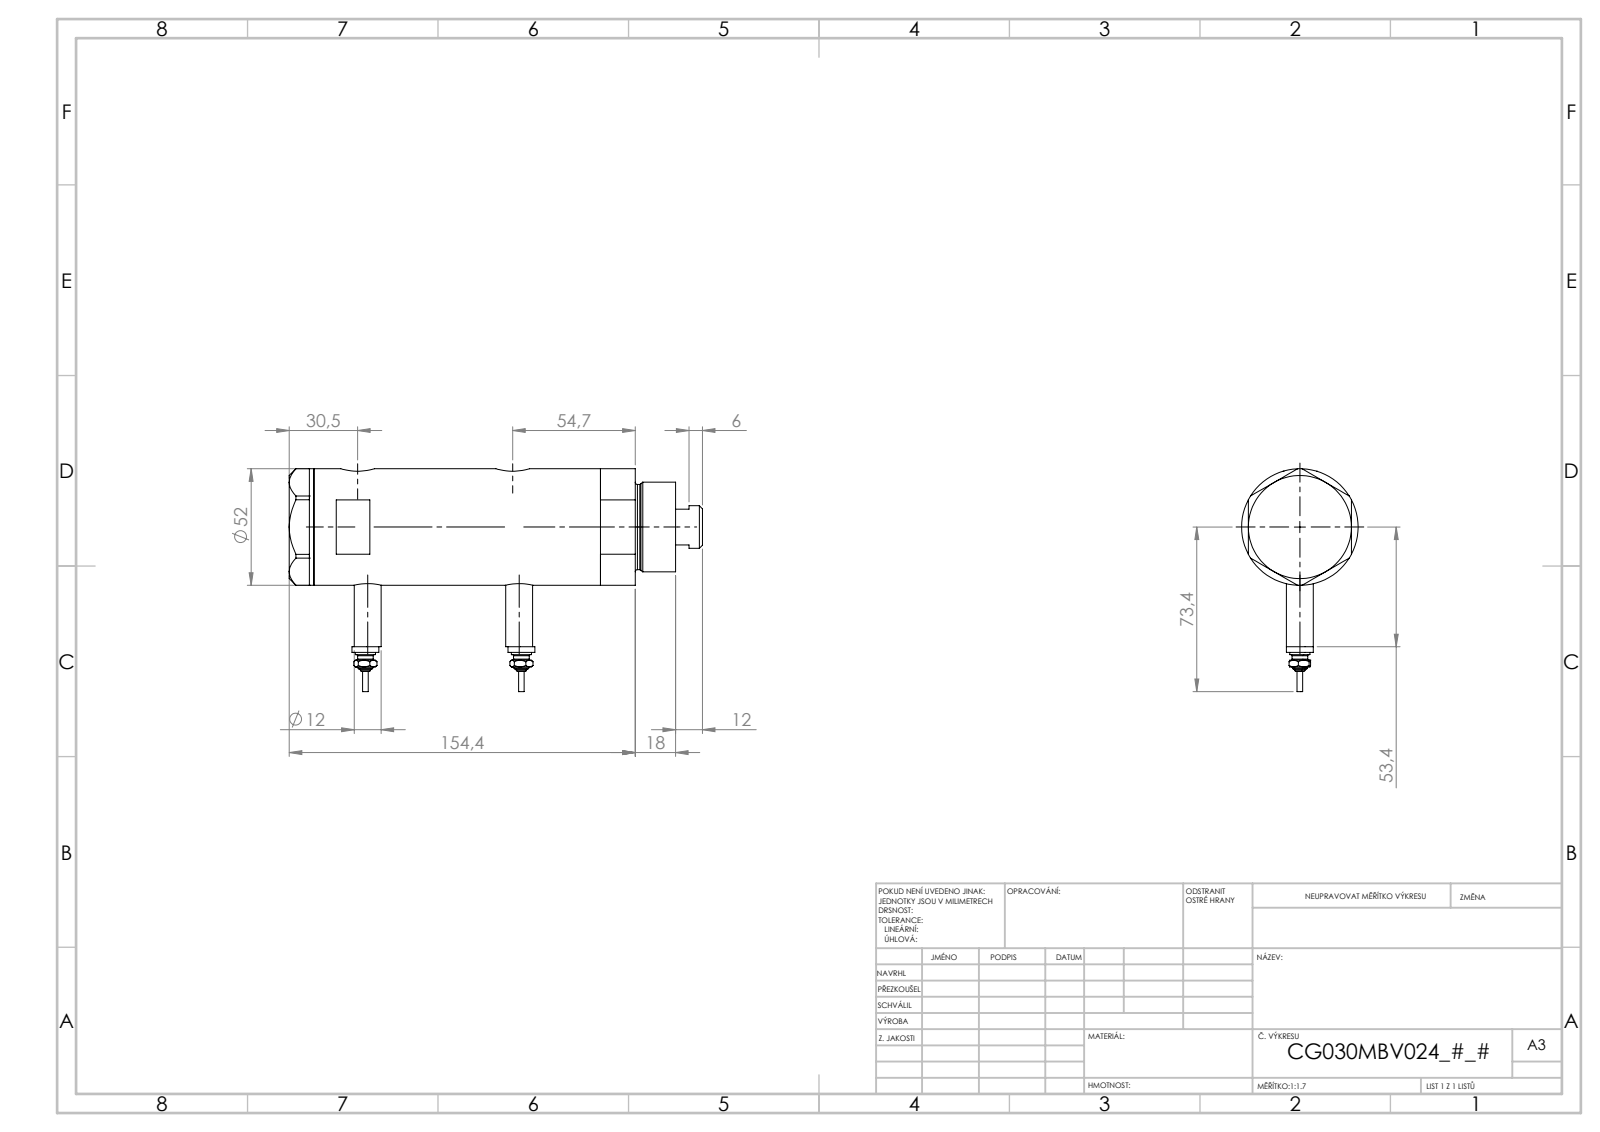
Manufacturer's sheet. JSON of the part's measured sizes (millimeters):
{"part_name": "V270CG_VC; Switch; V270CG_MIDDLE; V270CG_BACK (+1 more)", "step_written_by": "SolidWorks 2019 (CONFIG_CONTROL_DESIGN)", "units": "millimeters", "bodies": {"solids": 6, "faces": 226, "planar": 93, "cylindrical": 69, "other": 64}, "overall_size": [184.4, 99.4, 52], "volume_mm3": 343291, "surface_area_mm2": 80102, "round_holes": [[9.73, 2], [12.5, 2], [15, 2], [6.5, 1], [20, 1], [21.5, 1], [30, 1], [33, 1], [44, 1]], "round_bosses_or_shafts": [[12, 4], [9, 2], [7, 2], [4.5, 2], [2.5, 2], [52, 1], [40, 1], [38, 1]], "face_to_face_distances": [91.5, 23.8, 67.7, 11, 34.8, 102.5, 46, 36.4, 138.9, 127.9], "hole_center_spacings": [2.9, 4.5, 64.7, 67.6, 69.2, 72.1]}
